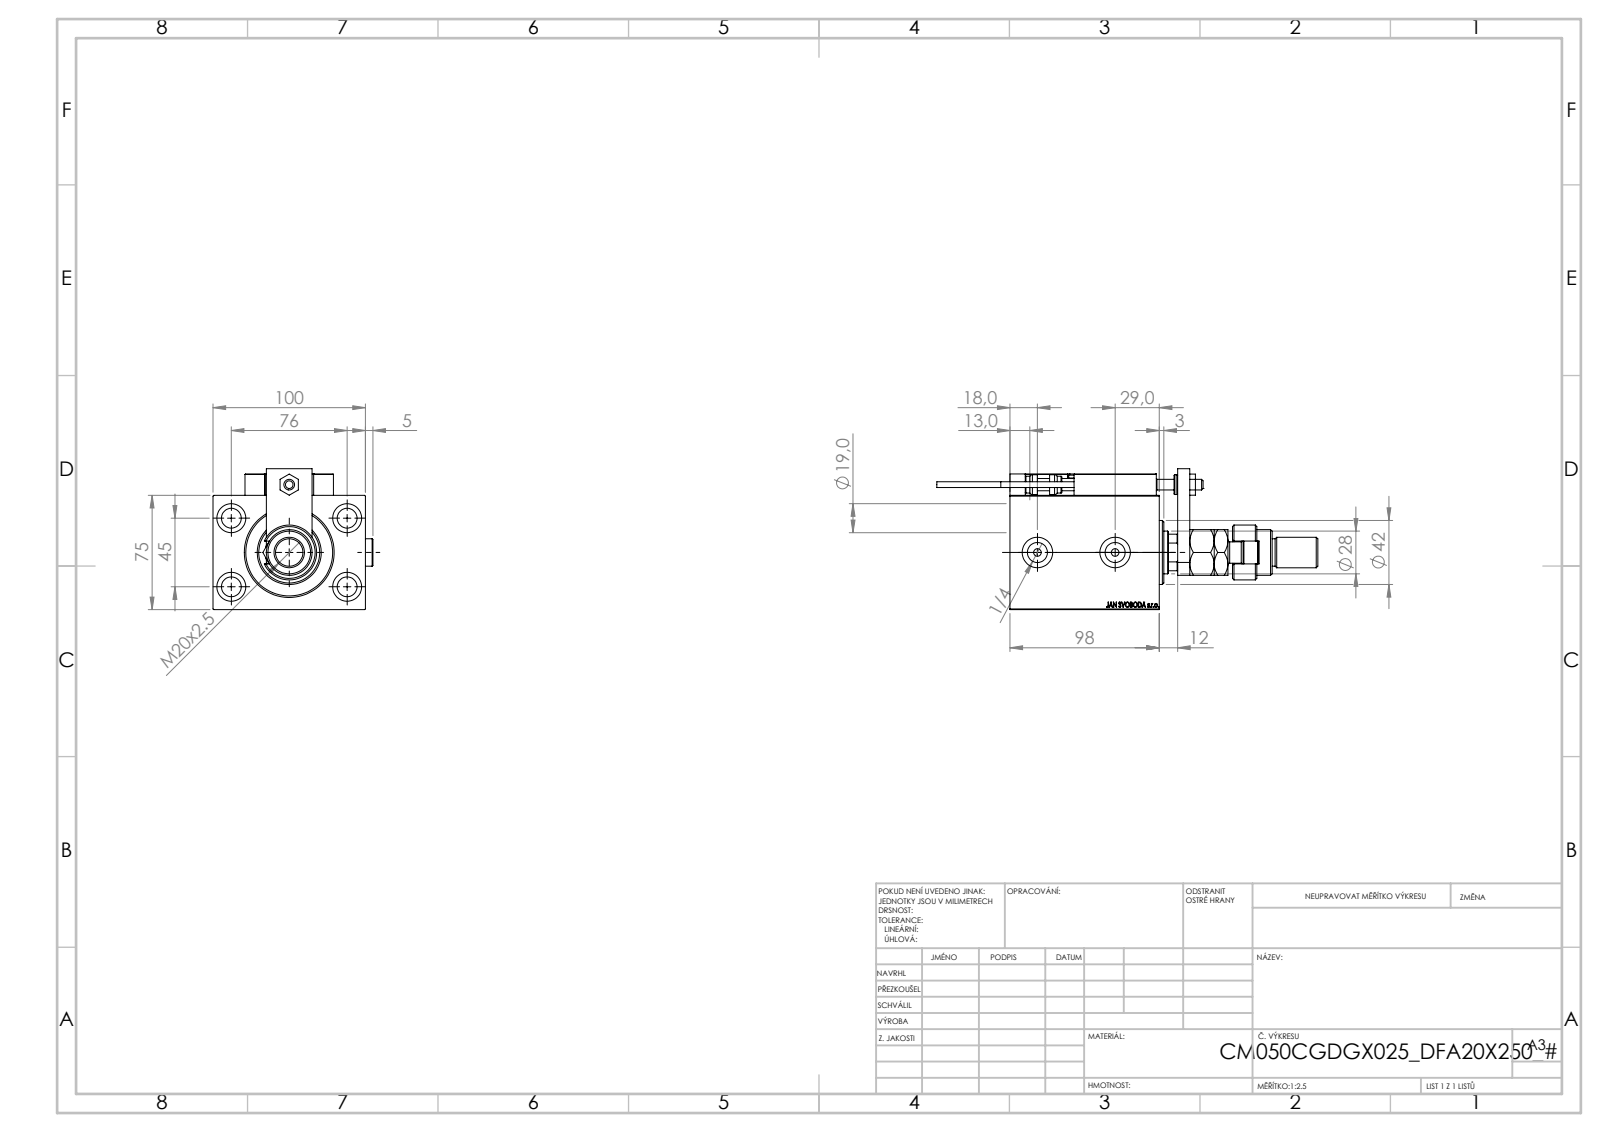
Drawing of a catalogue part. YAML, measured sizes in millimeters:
part_name: "TYC_L79; Zatka_OIL_PORT; V450CM_C_Body; ALLEN BOLT D5 (+7 more)"
step_written_by: "SolidWorks 2019 (CONFIG_CONTROL_DESIGN)"
units: millimeters
bodies: {solids: 27, faces: 1424, planar: 623, cylindrical: 219, other: 582}
overall_size: [250, 104.9, 92.5]
volume: 733604
surface_area: 148473
round_holes:
  - {diameter: 8, count: 5}
  - {diameter: 3.2, count: 4}
  - {diameter: 4, count: 4}
  - {diameter: 5, count: 4}
  - {diameter: 13, count: 4}
  - {diameter: 19, count: 4}
  - {diameter: 20, count: 3}
  - {diameter: 13.16, count: 2}
  - {diameter: 7, count: 1}
  - {diameter: 18.5, count: 1}
  - {diameter: 28, count: 1}
  - {diameter: 31.5, count: 1}
round_bosses_or_shafts:
  - {diameter: 18, count: 3}
  - {diameter: 5, count: 2}
  - {diameter: 3.8, count: 2}
  - {diameter: 42, count: 1}
  - {diameter: 36, count: 1}
  - {diameter: 30, count: 1}
  - {diameter: 22, count: 1}
  - {diameter: 14, count: 1}
partial_cylinders:
  - {radius: 0.3, count: 30}
  - {radius: 3, count: 2}
  - {radius: 7.5, count: 1}
  - {radius: 12, count: 1}
  - {radius: 13.5, count: 1}
face_to_face_distances: [75, 14, 100, 98, 25, 12, 84, 20, 24, 32]
hole_center_spacings: [44.16, 11.37, 20, 29.59, 29.69, 36.06, 42.19, 43.91]
